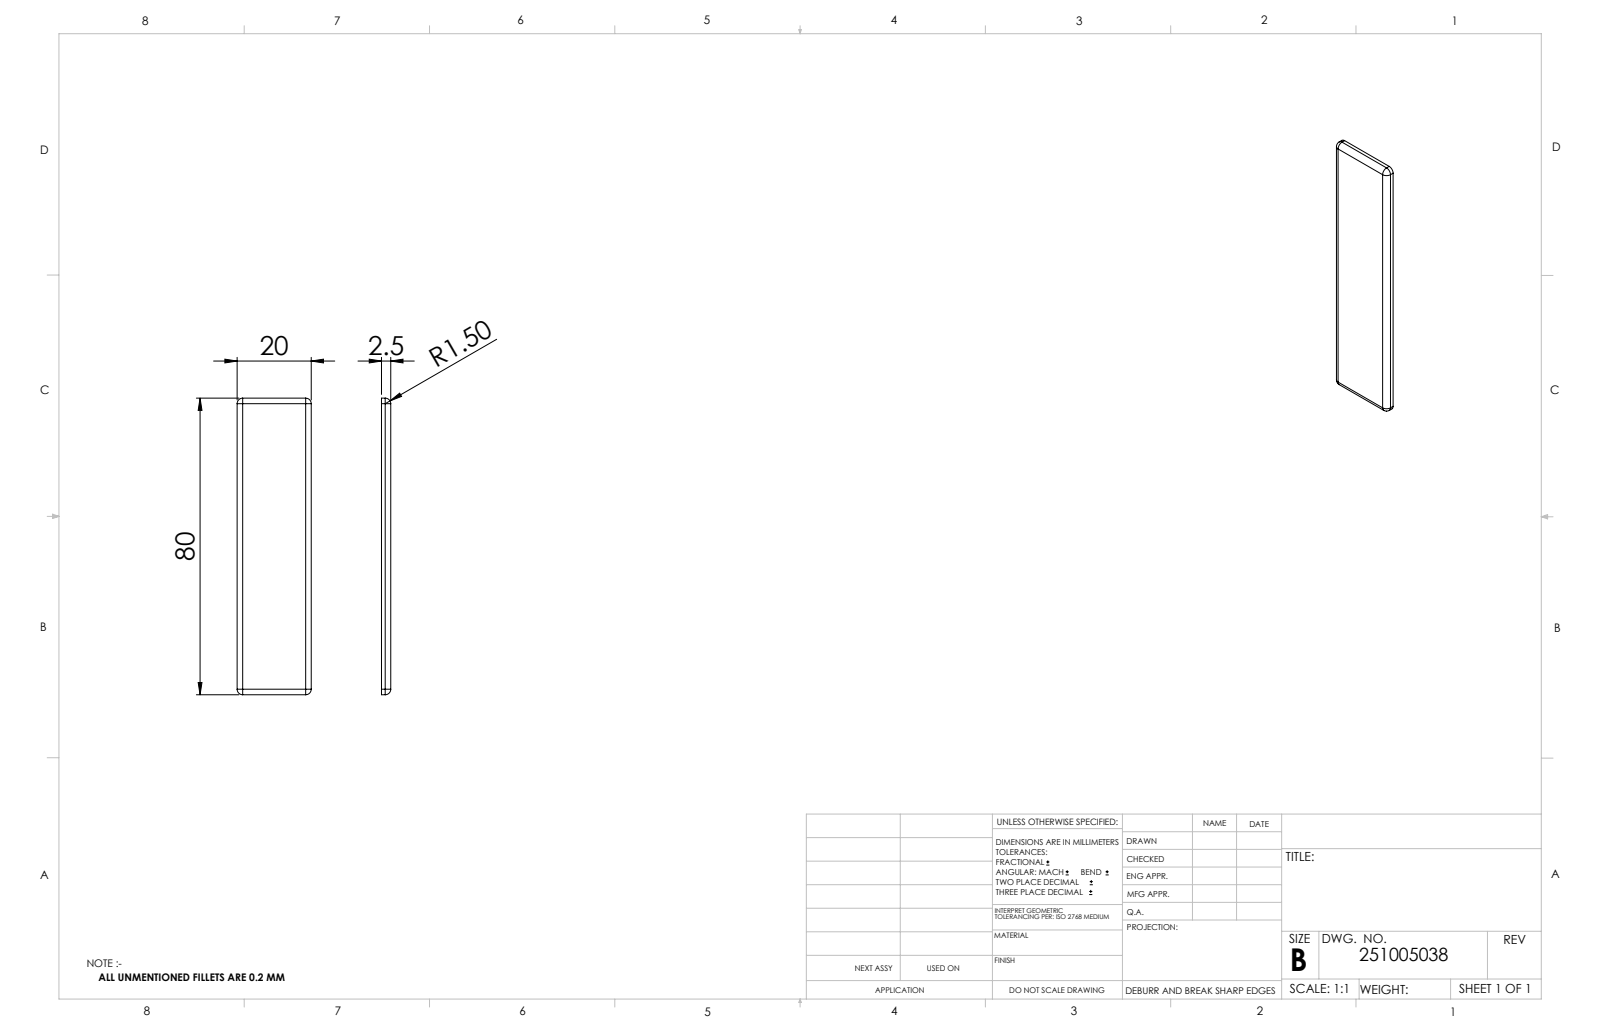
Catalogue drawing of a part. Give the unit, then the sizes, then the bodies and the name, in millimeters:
Units: millimetres
Overall size (bounding box): 80 × 20 × 2.5
Partial cylindrical surfaces — rounded edges, fillets, slot ends (radius × count): R1.5 ×8
Main face-to-face distances: 2.5, 20, 80
Volume: 3 901 mm³ · Surface area: 3 562 mm²
Bodies: 1 solid, 18 faces (6 planar, 8 cylindrical, 4 other)
Part name (STEP PRODUCT): 251005038_c_1
STEP written by: SolidWorks 2014 (CONFIG_CONTROL_DESIGN)
